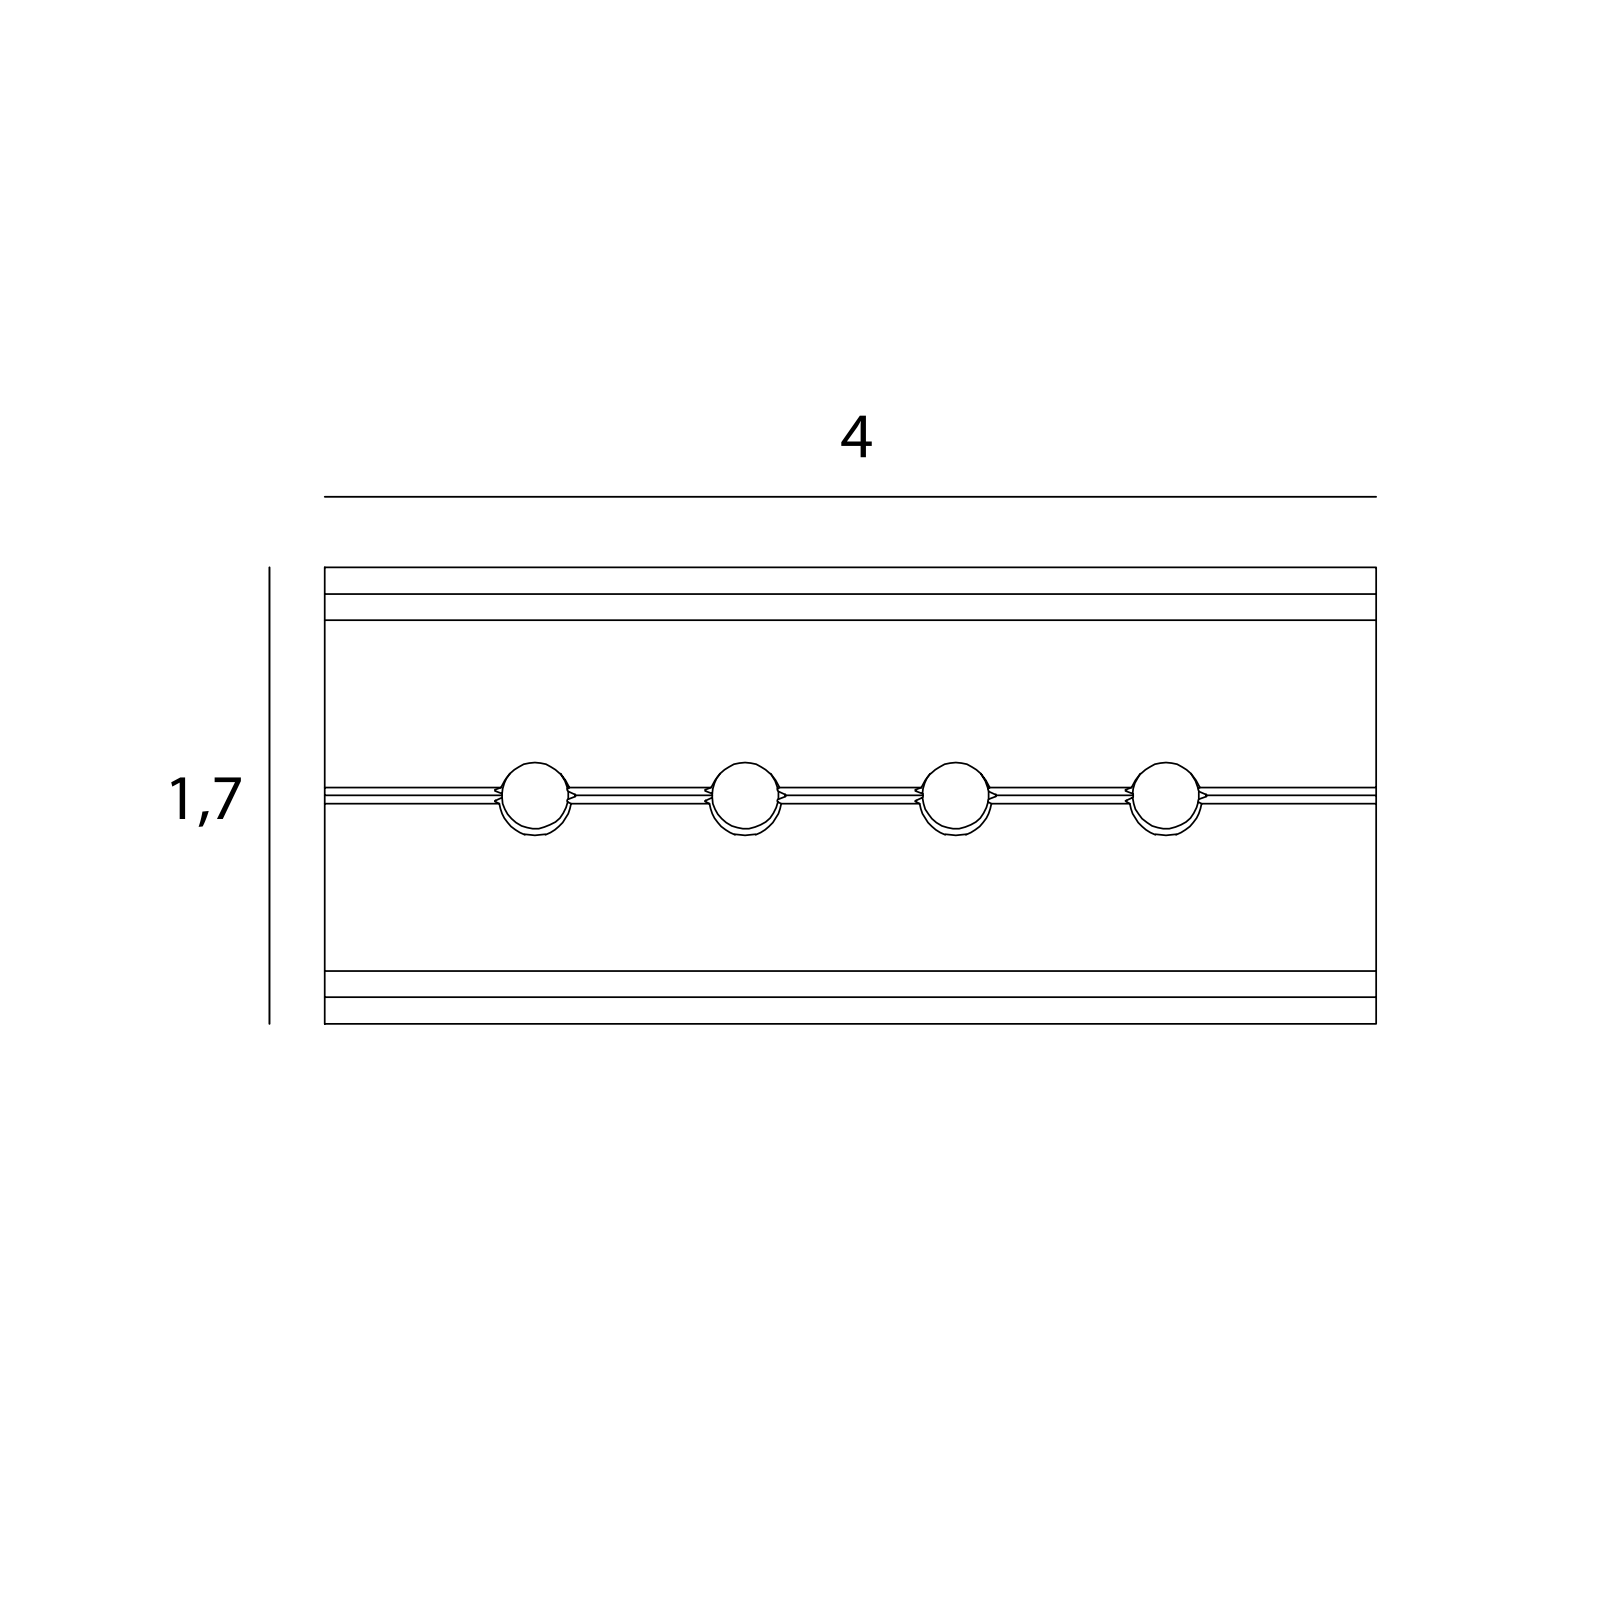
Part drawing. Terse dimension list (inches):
name: NA0013 v3
written by: Autodesk Translation Framework v14.24.0.0 (AUTOMOTIVE_DESIGN)
unit: in
bodies: 1 solid, 97 faces (25 planar, 48 cylindrical, 24 other)
size: 1.575 × 0.683 × 0.081
volume: 0.069 in³; area: 2.61 in²
holes: 4× ⌀0.1, 4× ⌀0.122
face distances: 0.079, 0.026, 0.053, 0.033, 0.045, 0.079, 0.604, 0.525, 1.575, 0.683
hole spacings: 0.315, 0.63, 0.945
